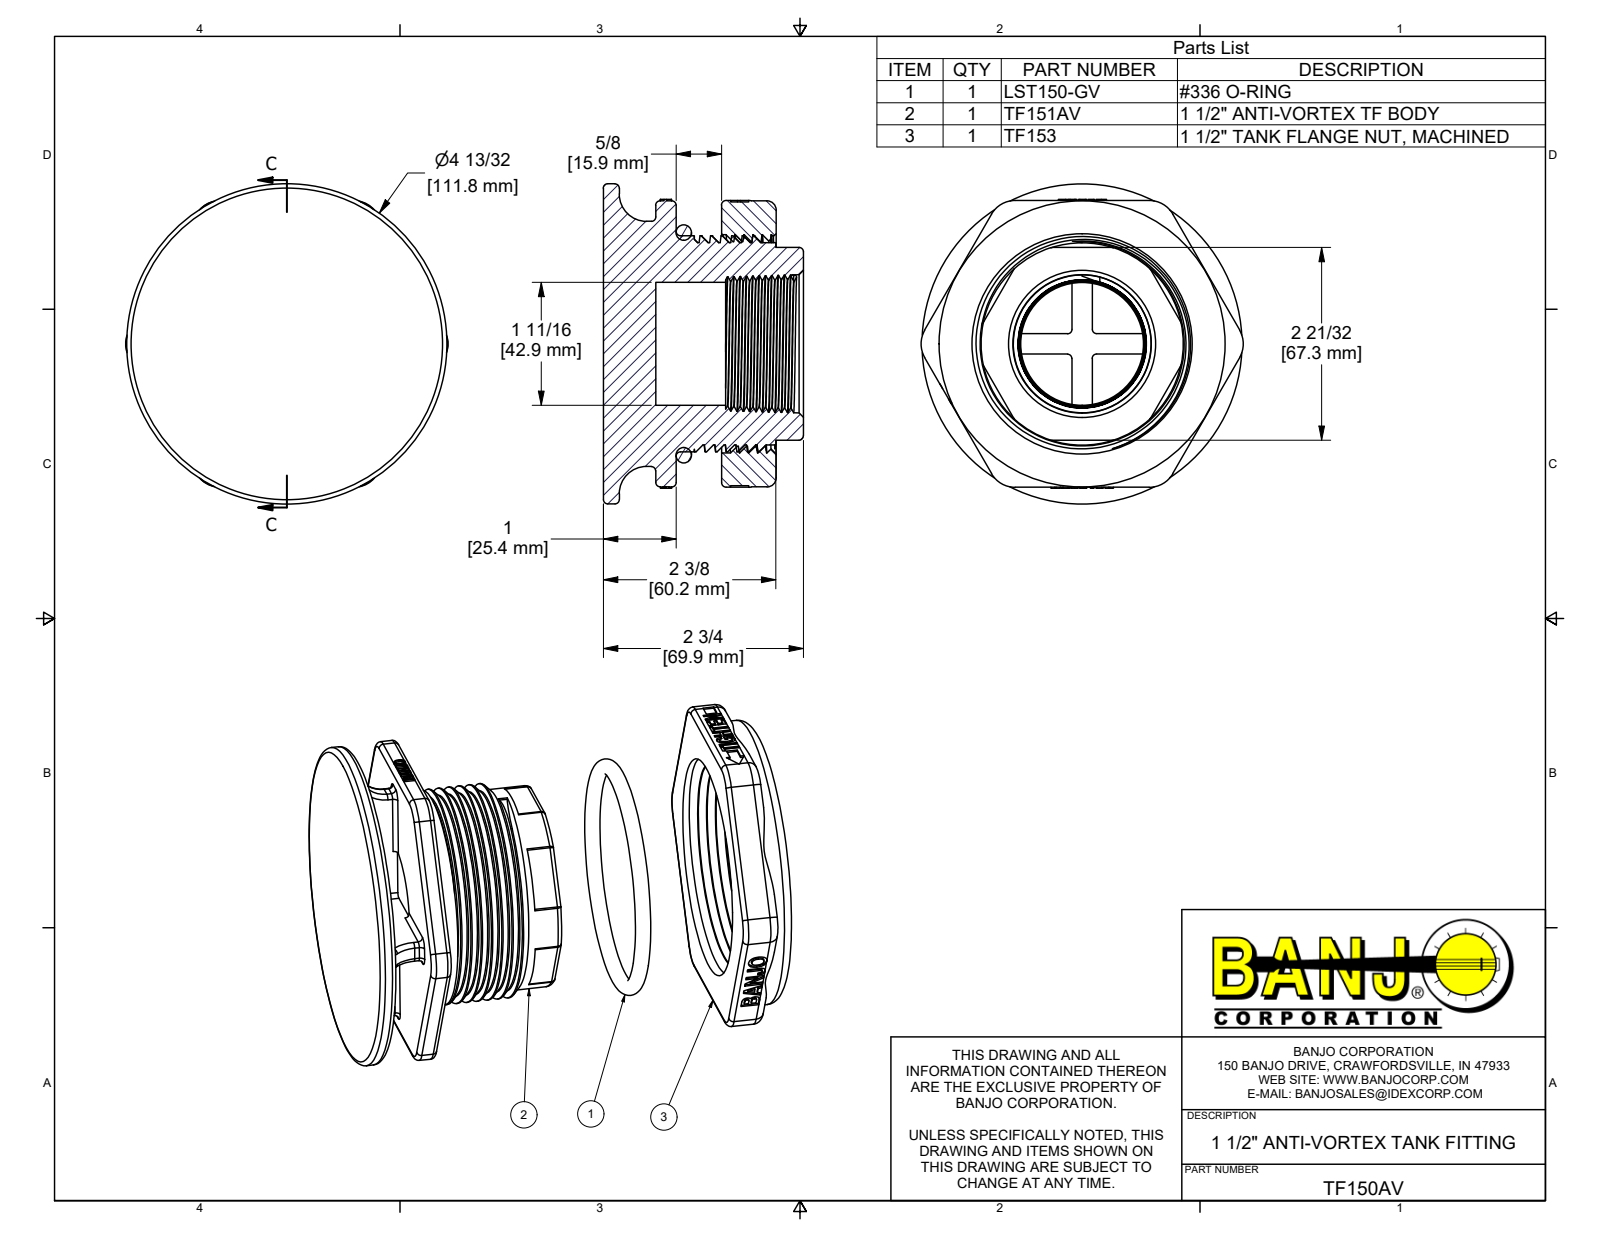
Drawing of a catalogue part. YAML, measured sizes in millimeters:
part_name: "TF150AV; TF151AV; TF153-OBS; LST150-GV (+1 more)"
step_written_by: "Autodesk Inventor 2017 (AUTOMOTIVE_DESIGN)"
units: millimeters
bodies: {solids: 8, faces: 876, planar: 524, cylindrical: 117, other: 235}
overall_size: [112.61, 111.76, 69.85]
volume: 314217
surface_area: 90837
round_holes:
  - {diameter: 42.93, count: 1}
  - {diameter: 71.3, count: 1}
  - {diameter: 76.2, count: 1}
round_bosses_or_shafts:
  - {diameter: 111.76, count: 1}
  - {diameter: 99.82, count: 1}
  - {diameter: 75.44, count: 1}
  - {diameter: 70.61, count: 1}
partial_cylinders:
  - {radius: 1.52, count: 54}
  - {radius: 9.53, count: 16}
  - {radius: 1.59, count: 6}
  - {radius: 3.17, count: 6}
  - {radius: 21.5, count: 1}
  - {radius: 25.4, count: 1}
face_to_face_distances: [5.59, 12.7, 18.29, 35.69, 15.88, 41.28, 22.99, 7.11, 19.81, 25.4]
